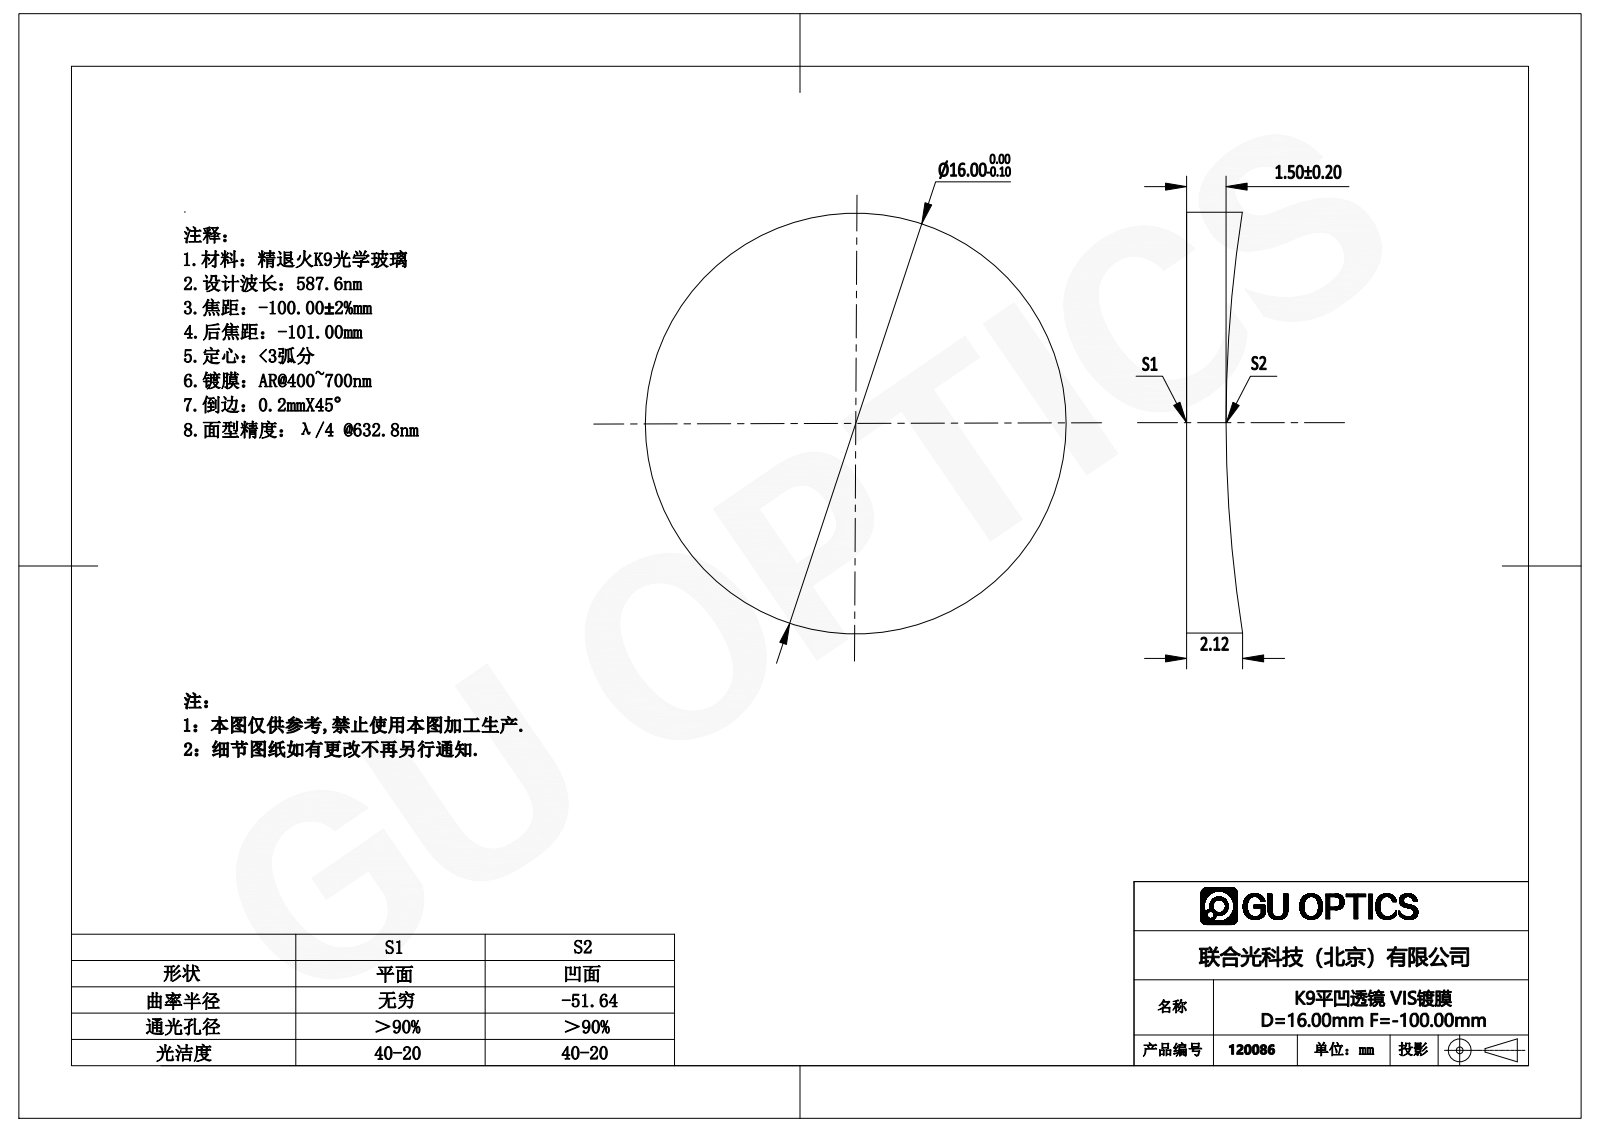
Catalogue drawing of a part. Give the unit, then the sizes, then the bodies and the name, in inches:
Units: inches
Overall size (bounding box): 0.63 × 0.63 × 0.083
Round bosses / shafts (diameter × count): ⌀0.63 ×1
Volume: 0.022 in³ · Surface area: 0.791 in²
Bodies: 1 solid, 5 faces (1 planar, 2 cylindrical, 2 other)
Part name (STEP PRODUCT): 120026
STEP written by: SolidWorks 2016 (AUTOMOTIVE_DESIGN)
